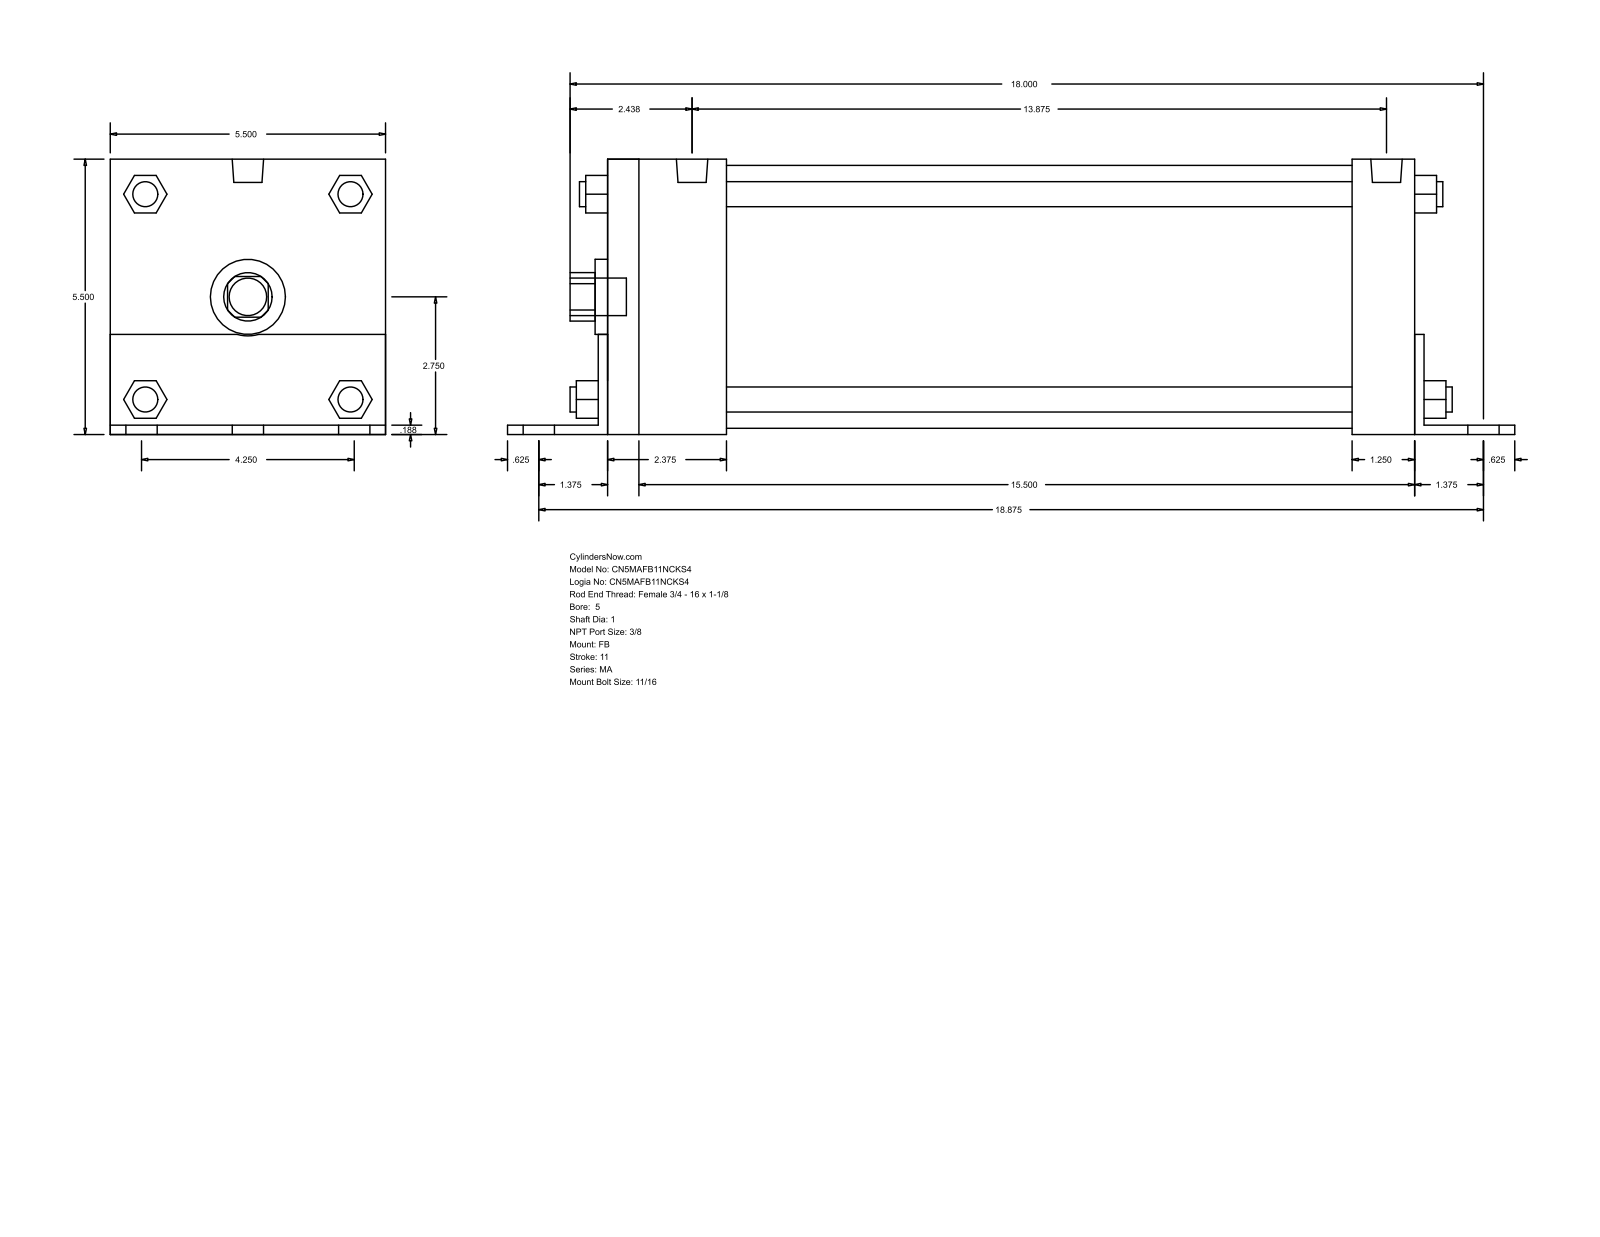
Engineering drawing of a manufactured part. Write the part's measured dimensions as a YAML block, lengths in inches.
part_name: "MA_FB__0500_1"
step_written_by: "GSSL Pune (CONFIG_CONTROL_DESIGN)"
units: inches
bodies: {solids: 0, faces: 140, planar: 105, cylindrical: 35, other: 0}
overall_size: [20.125, 5.502, 5.5]
round_holes:
  - {diameter: 1, count: 1}
  - {diameter: 1.5, count: 1}
  - {diameter: 5.25, count: 1}
round_bosses_or_shafts:
  - {diameter: 0.687, count: 6}
  - {diameter: 0.5, count: 4}
  - {diameter: 0.437, count: 4}
  - {diameter: 0.627, count: 2}
  - {diameter: 0.75, count: 1}
partial_cylinders:
  - {radius: 0.484, count: 1}
  - {radius: 0.78, count: 1}
face_to_face_distances: [5.5, 0.187, 5.502, 0.185, 5.315, 16.125, 0.188, 16.313, 16.312, 16.5]
